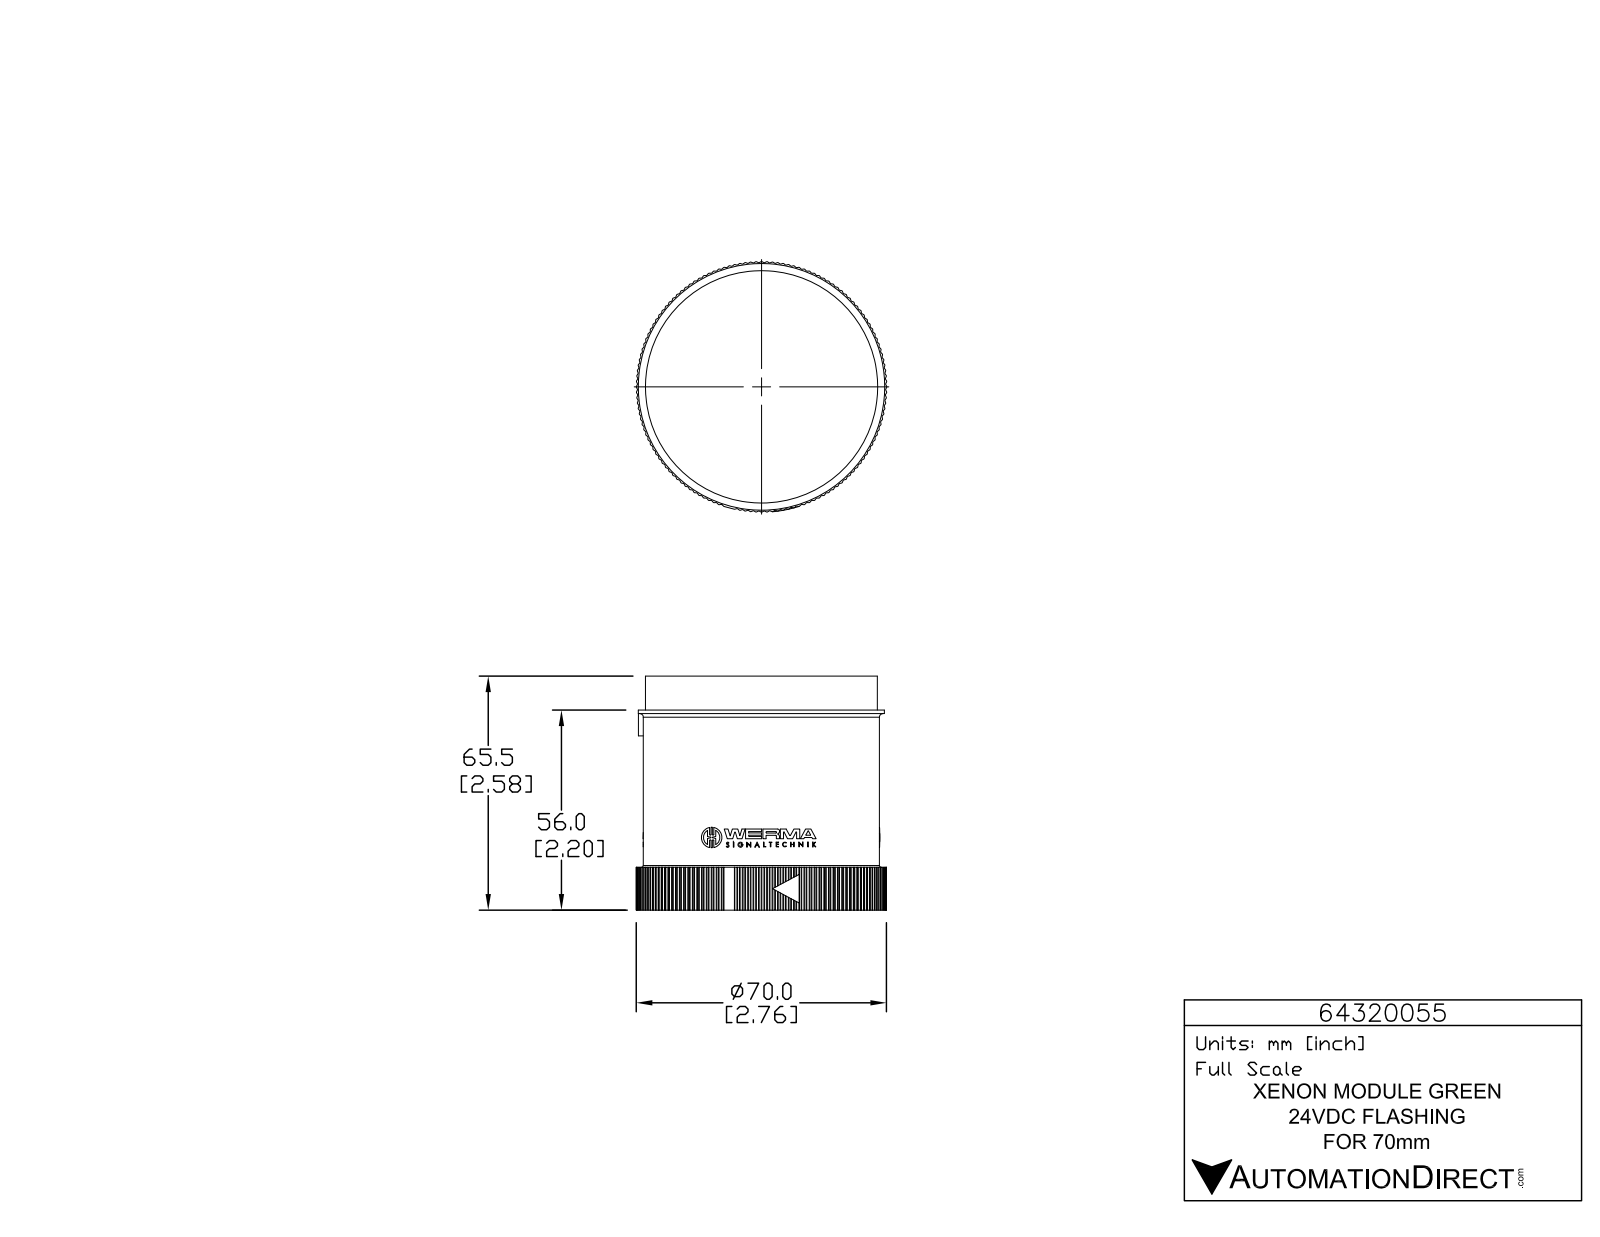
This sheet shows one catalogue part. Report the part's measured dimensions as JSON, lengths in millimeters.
{"part_name": "64320055", "step_written_by": "SolidWorks 2015 (AUTOMOTIVE_DESIGN)", "units": "millimeters", "bodies": {"solids": 1, "faces": 1400, "planar": 832, "cylindrical": 563, "other": 5}, "overall_size": [70.2, 70.2, 65.5], "volume_mm3": 197000, "surface_area_mm2": 24180, "round_holes": [[1, 3], [65.4, 1]], "round_bosses_or_shafts": [[5.7, 3], [1.4, 3], [69, 1], [66.2, 1], [65, 1]], "partial_cylinders_radius": [[0.2, 285], [0.2, 6], [0.2, 6], [0.2, 6], [3.3, 6], [0.1, 3], [0.1, 3], [0.2, 3]], "face_to_face_distances": [55.9, 62.3, 9.6, 65.5, 56, 46.4, 9.5, 62.3, 12, 2.4]}
